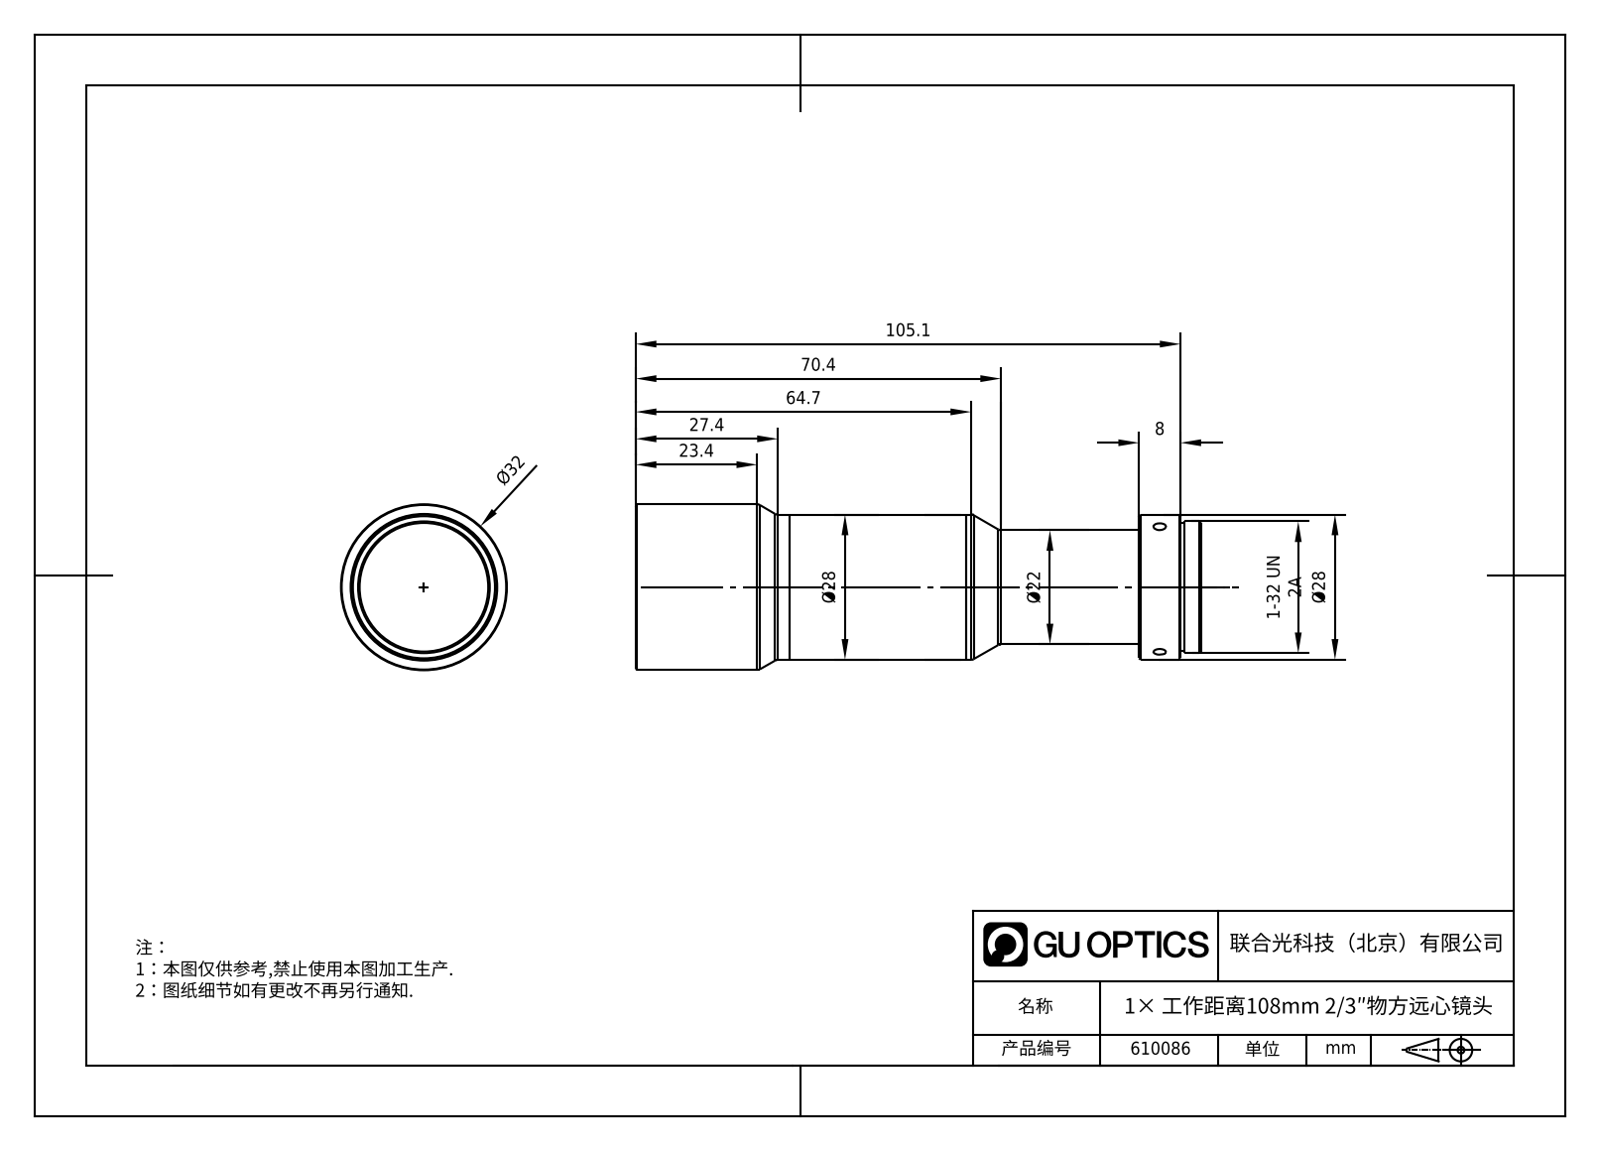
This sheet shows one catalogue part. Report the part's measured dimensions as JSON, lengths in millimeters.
{"part_name": "WWH10-108ATV3", "step_written_by": "SolidWorks 2017 (CONFIG_CONTROL_DESIGN)", "units": "millimeters", "bodies": {"solids": 1, "faces": 37, "planar": 5, "cylindrical": 12, "other": 20}, "overall_size": [109.1, 32, 32], "volume_mm3": 64489, "surface_area_mm2": 11104, "round_bosses_or_shafts": [[32, 1], [28, 1], [25.4, 1], [24.4, 1], [22, 1]], "face_to_face_distances": [109.1, 97.1, 12, 105.1, 8, 4, 105.9, 8.8, 0.8, 3.2]}
